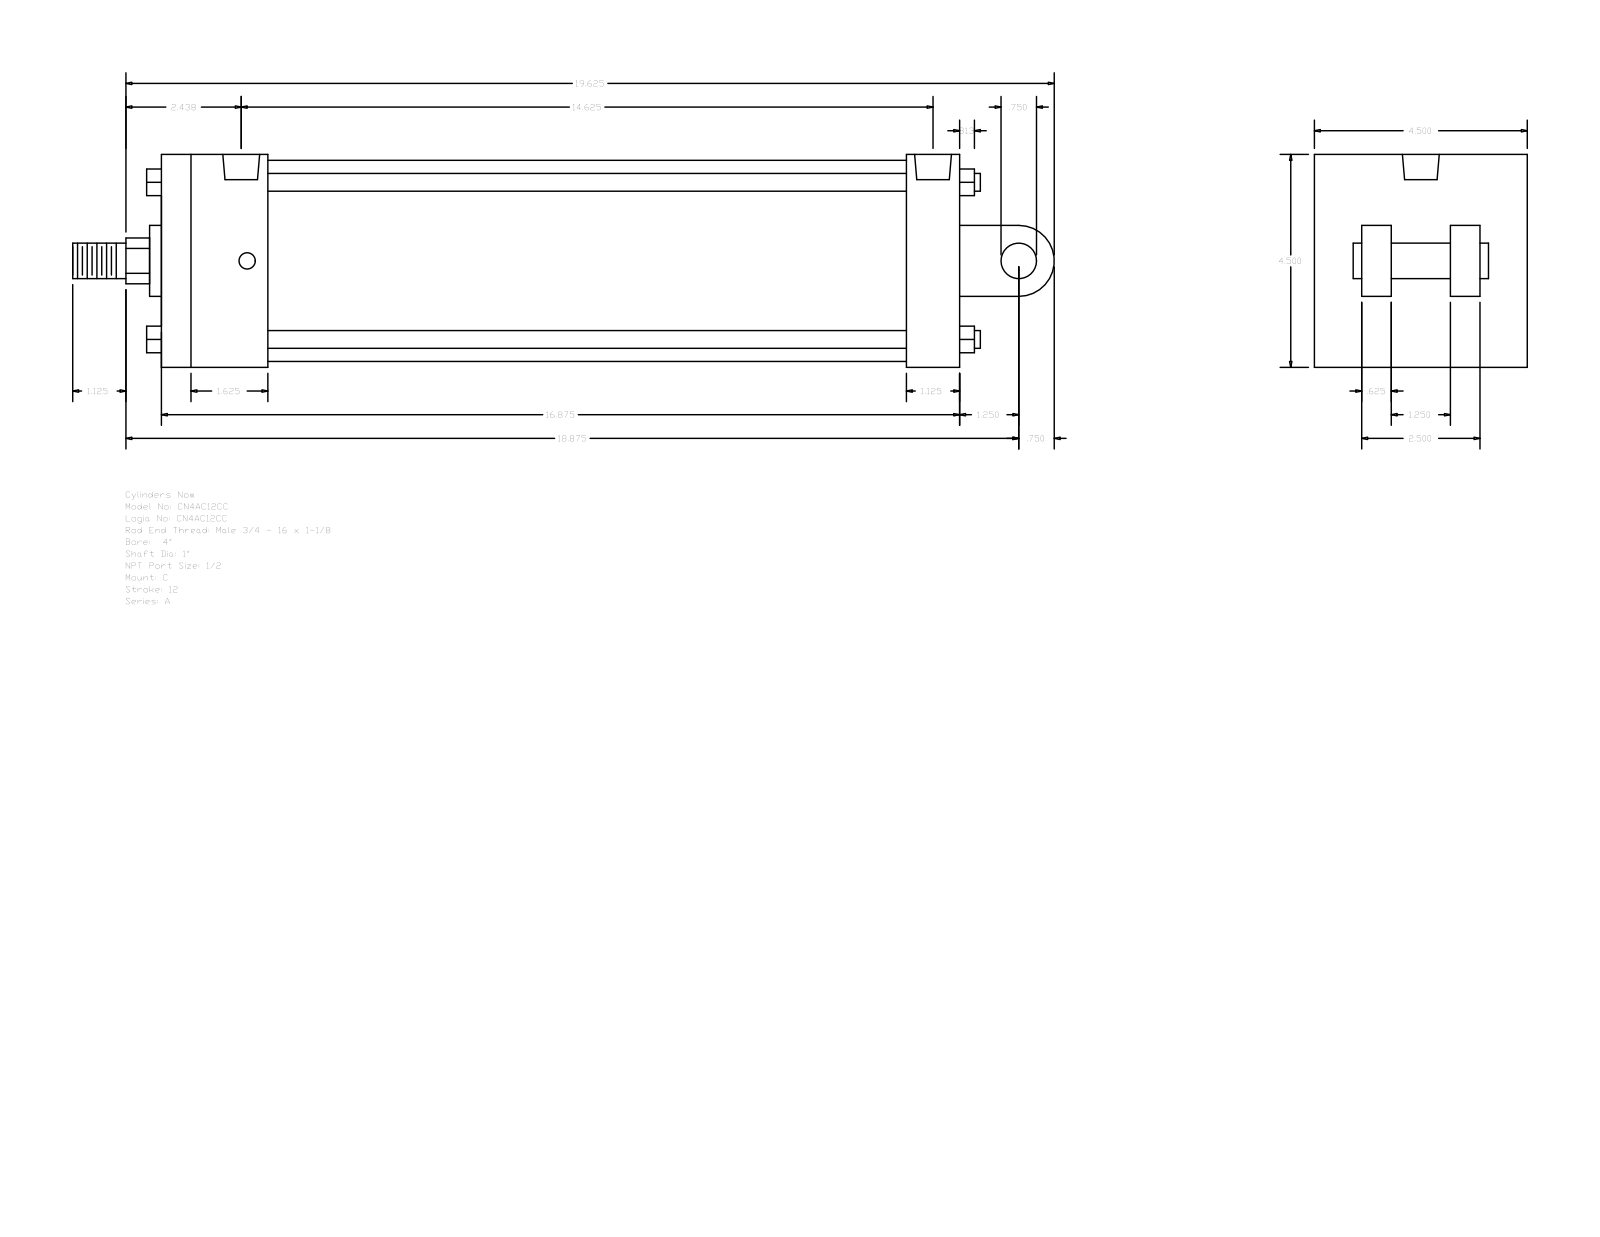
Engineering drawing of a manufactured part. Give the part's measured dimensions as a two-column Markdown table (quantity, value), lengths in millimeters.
| quantity | value |
| --- | --- |
| part name | A_C__0400_1 |
| STEP written by | GSSL Pune (CONFIG_CONTROL_DESIGN) |
| units | millimeters |
| bodies | 0 solids, 135 faces (102 planar, 33 cylindrical, 0 other) |
| overall size | 527.05 × 114.3 × 114.3 |
| round holes (diameter × count) | 8.73 × 4, 19.77 × 2 |
| round bosses / shafts (diameter × count) | 9.53 × 4, 19.05 × 2, 107.95 × 1, 38.1 × 1, 25.4 × 1 |
| partial cylindrical surfaces (radius × count) | 12.29 × 1, 19.05 × 1 |
| main face-to-face distances | 114.3, 428.63, 73.03, 400.05, 28.58, 57.15, 342.9, 371.48, 41.27, 38.1 |
| hole center spacings | 3.18, 365.12, 368.3, 371.48 |
